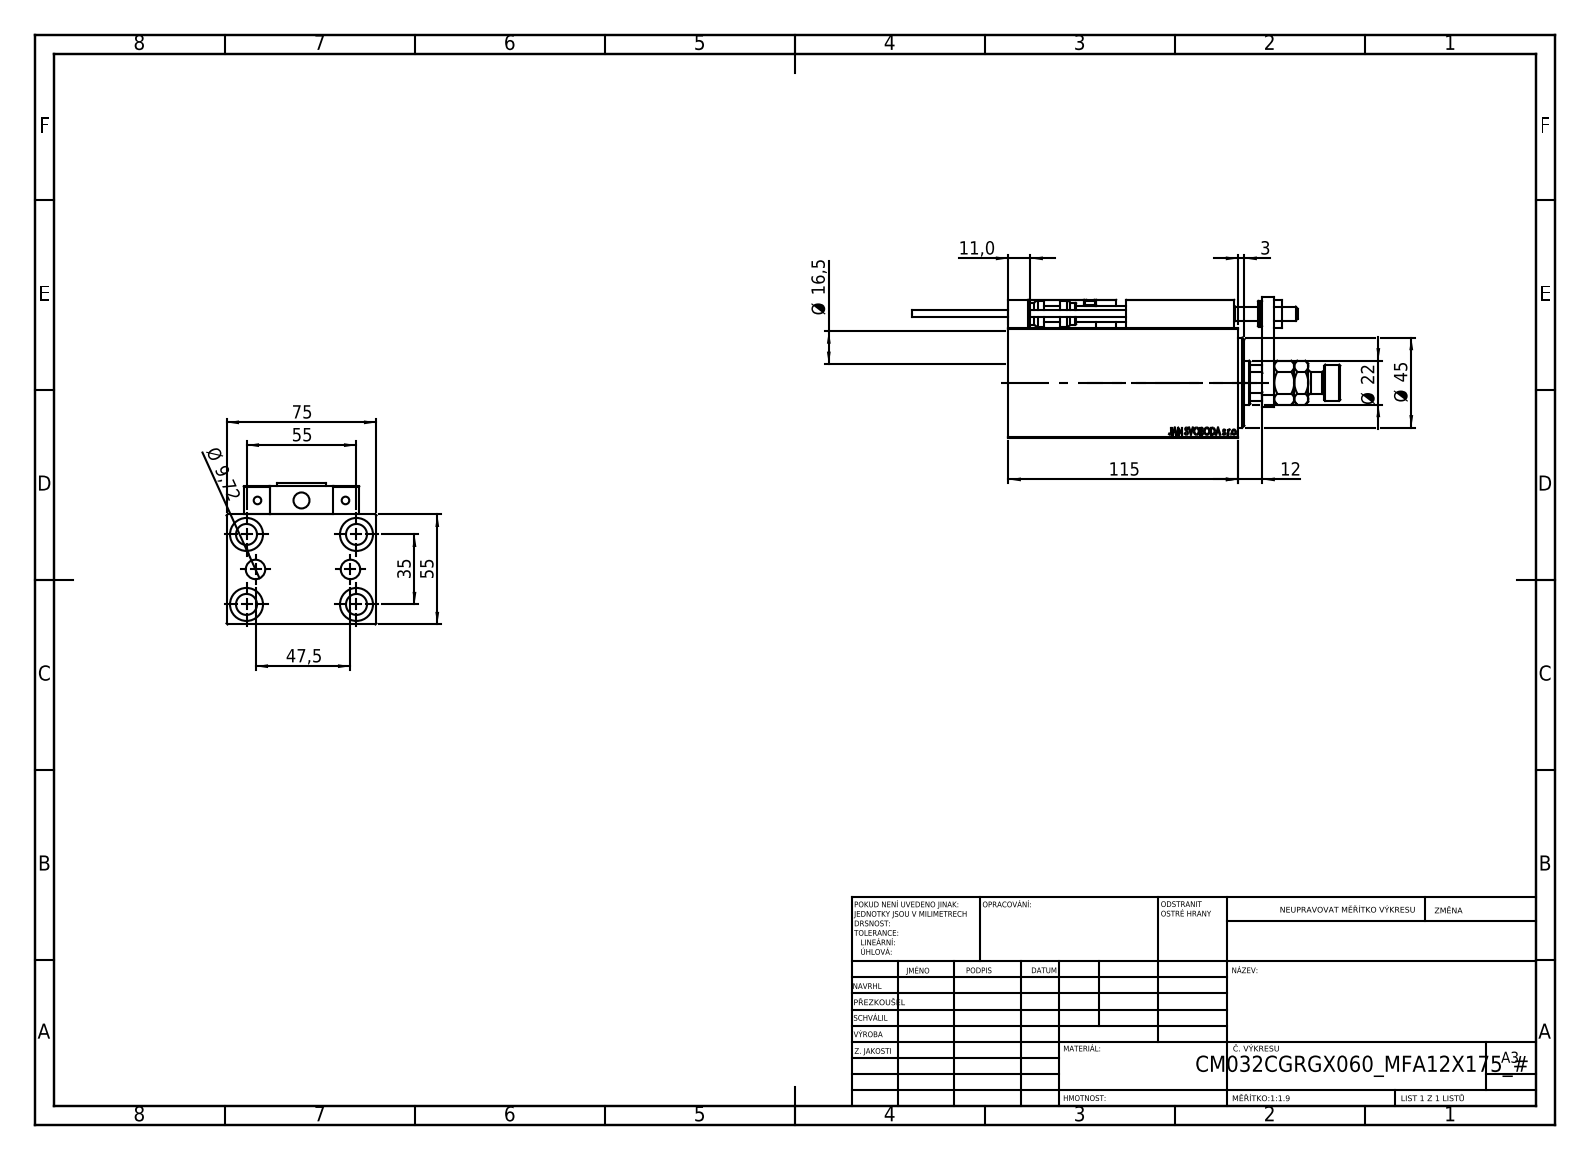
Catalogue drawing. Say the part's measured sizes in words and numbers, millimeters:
The part is named "X_Y_MFA; V450CM_C_VCP; ZARAZKA; TYC_L79 (+8 more)". Its 3-D file was written by "SolidWorks 2019 (CONFIG_CONTROL_DESIGN)". It is 24 solids with 1324 faces: 574 planar, 184 cylindrical and 566 other. Overall it measures 214 by 75 by 70.5 millimeters. Its volume is 459 750 cubic millimeters and its surface area 109 985 square millimeters. Round holes: 5 of diameter 8, 5 of diameter 10.5, 5 of diameter 16.5, 4 of diameter 3.2, 4 of diameter 4, 2 of diameter 5, 2 of diameter 9.72, 1 of diameter 7, 1 of diameter 22, 1 of diameter 25.5, 1 of diameter 32, 1 of diameter 34. Round bosses or shafts: 2 of diameter 11, 2 of diameter 5, 2 of diameter 3.8, 1 of diameter 18, 1 of diameter 13. Partial cylindrical surfaces (rounded edges, fillets, slot ends): 30 of radius 0.3, 2 of radius 3, 1 of radius 10.5. The main face-to-face distances are 55, 75, 14, 10, 12, 7, 3, 69, 5, 23. The hole center spacings are 32.6, 11.37, 17.76, 18.07, 20, 29.59, 29.69, 32.33.
